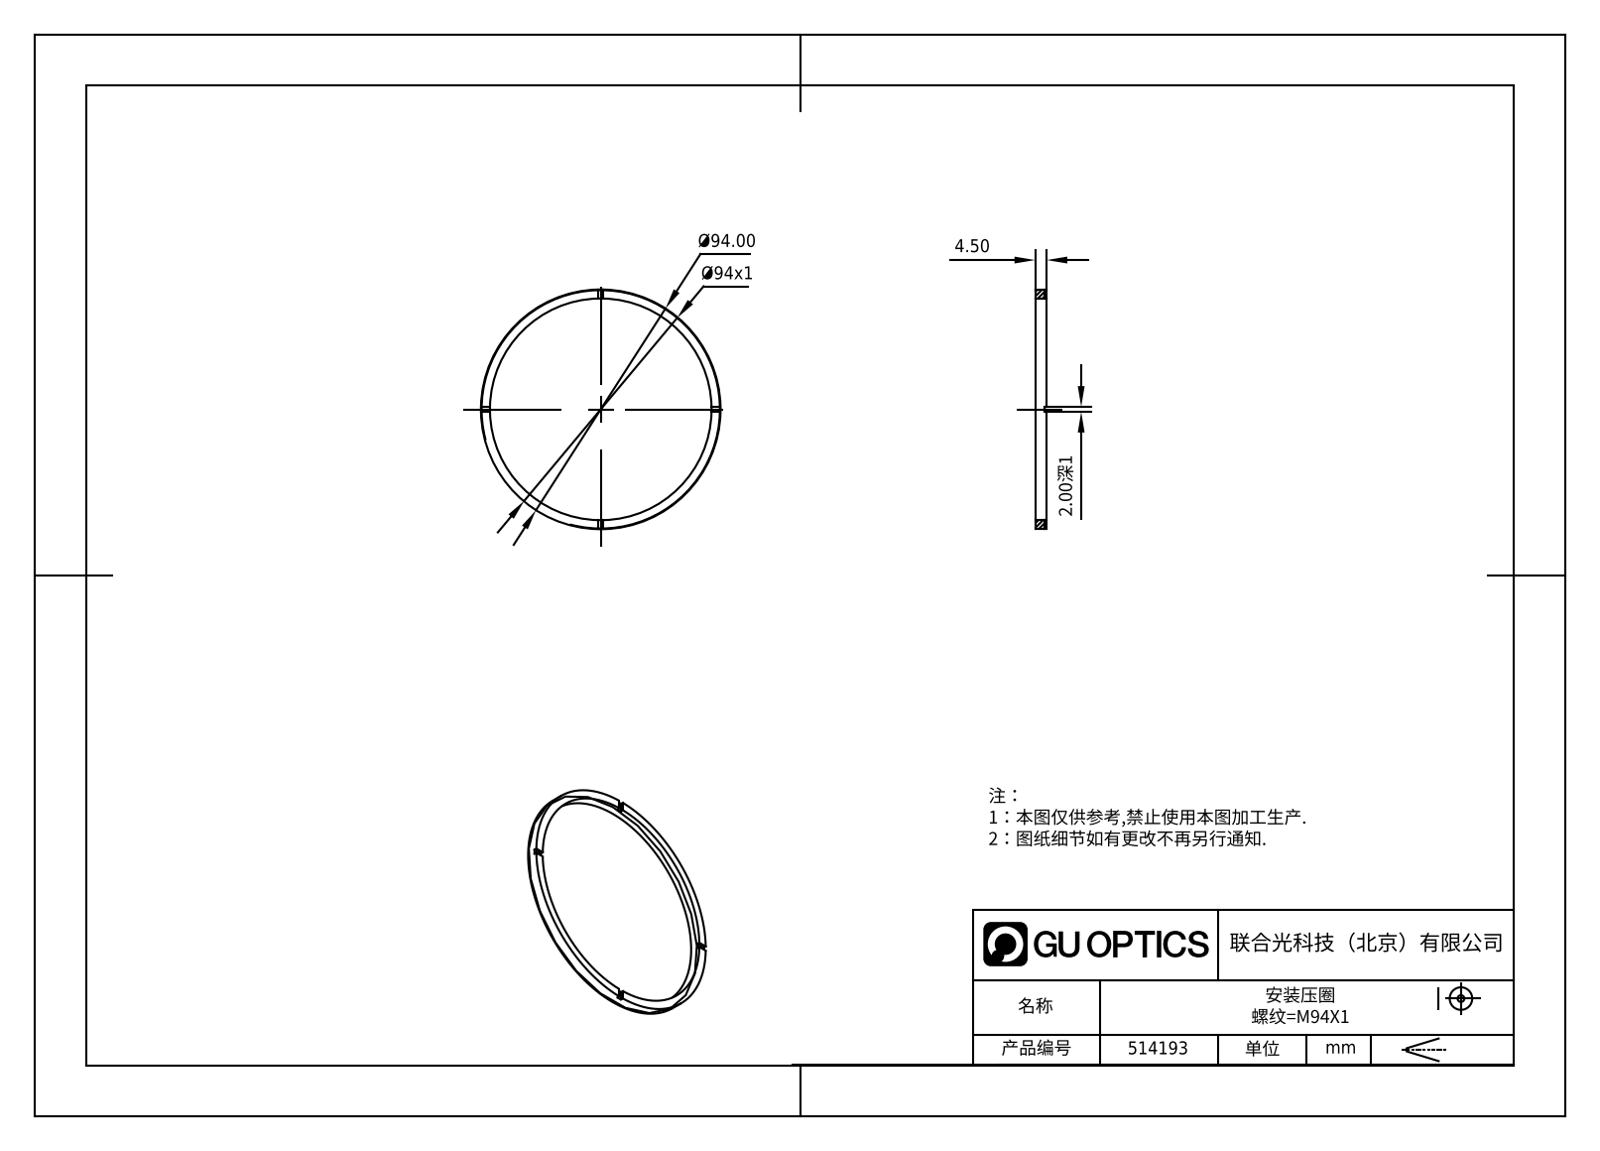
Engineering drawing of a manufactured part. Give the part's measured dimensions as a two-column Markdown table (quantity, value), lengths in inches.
| quantity | value |
| --- | --- |
| part name | 514193 |
| STEP written by | SolidWorks 2020 (CONFIG_CONTROL_DESIGN) |
| units | inches |
| bodies | 1 solid, 21 faces (17 planar, 4 cylindrical, 0 other) |
| overall size | 3.701 × 3.701 × 0.177 |
| volume | 0.272 in³ |
| surface area | 7.07 in² |
| round holes (diameter × count) | 3.425 × 1 |
| round bosses / shafts (diameter × count) | 3.701 × 1 |
| main face-to-face distances | 0.177, 0.138, 0.039, 0.079 |
